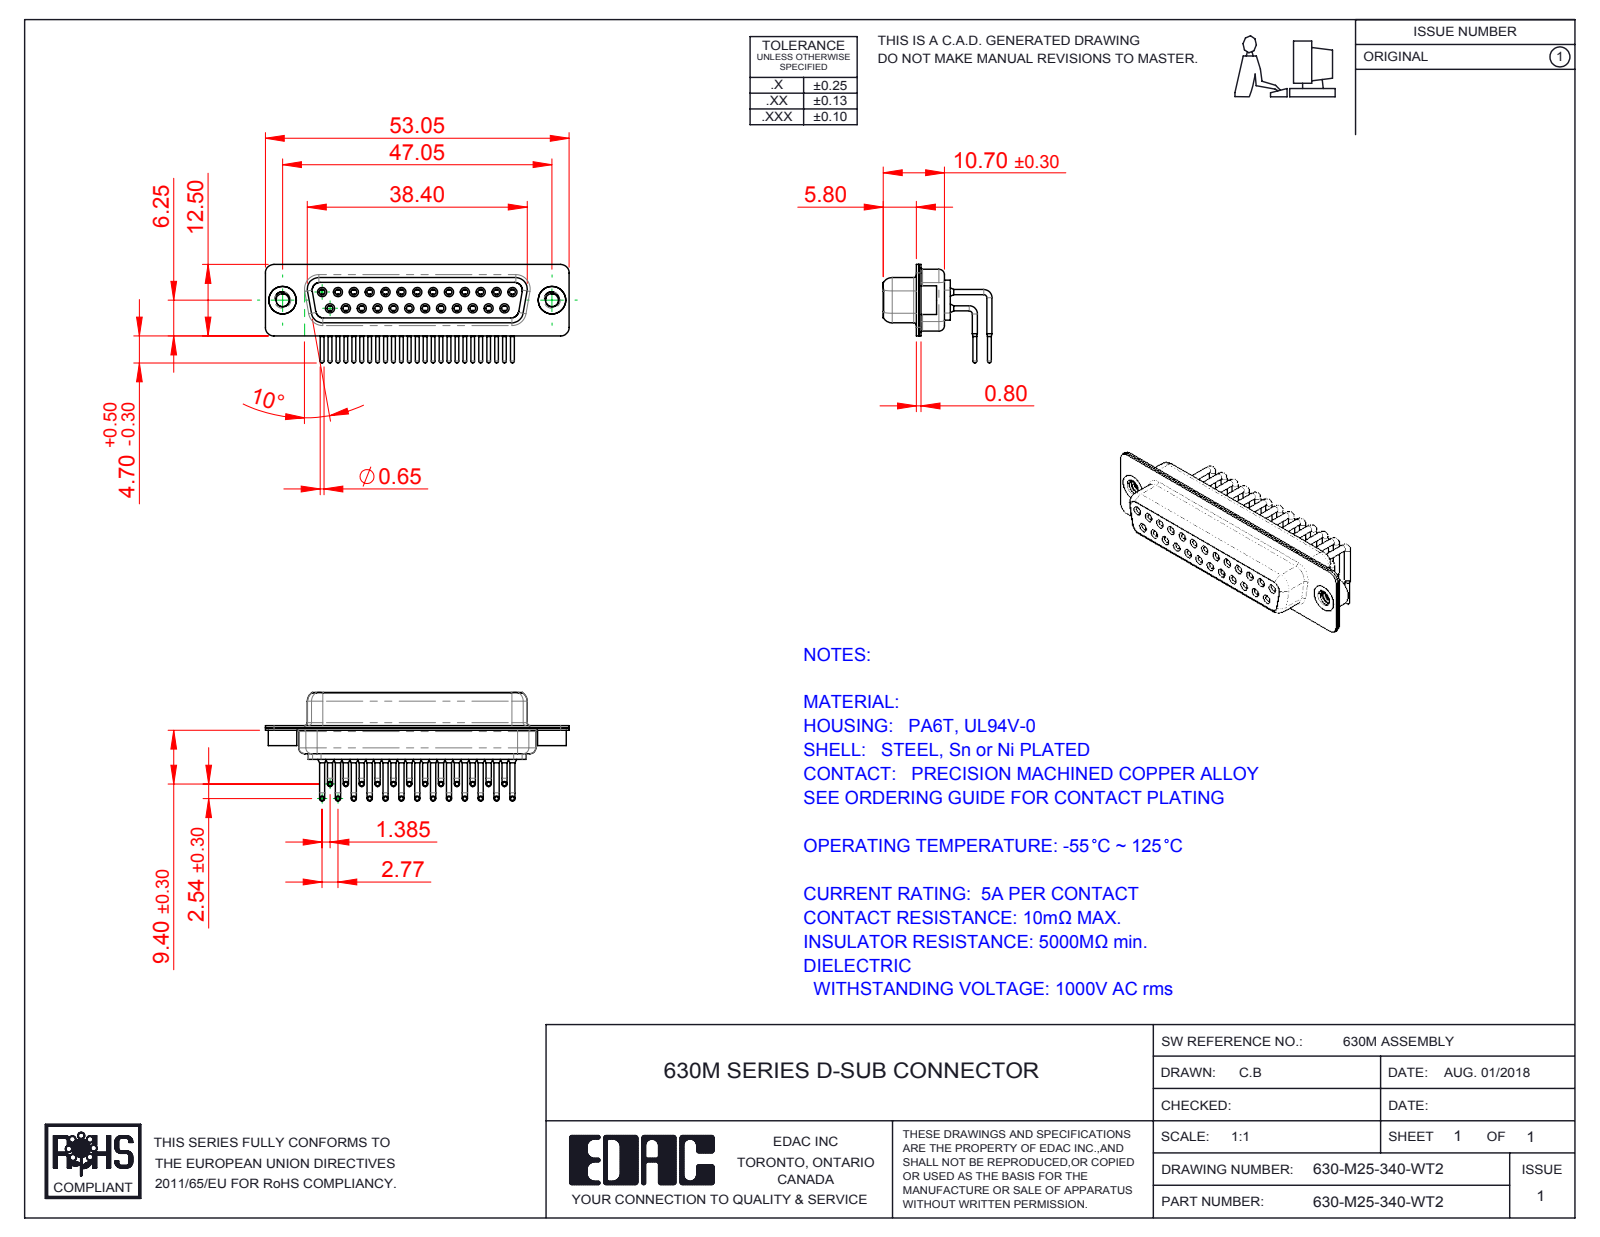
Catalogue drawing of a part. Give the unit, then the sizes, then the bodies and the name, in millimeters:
Units: millimetres
Overall size (bounding box): 53.05 × 18.99 × 17.2
Round holes (diameter × count): ⌀1 ×25, ⌀1.1 ×25, ⌀1.7 ×25, ⌀1.8 ×25, ⌀2 ×25, ⌀2.26 ×2, ⌀4 ×2, ⌀4.8 ×2
Round bosses / shafts (diameter × count): ⌀0.9 ×50, ⌀1.6 ×25, ⌀1.5 ×25, ⌀0.65 ×25, ⌀5 ×2, ⌀4.9 ×2
Partial cylindrical surfaces — rounded edges, fillets, slot ends (radius × count): R1.5 ×16, R2 ×12, R1.35 ×10, R1.6 ×8, R0.25 ×4, R0.5 ×4, R0.6 ×4, R0.65 ×4
Main face-to-face distances: 0.4, 1.45, 8.95, 6.2, 2.3, 1.9, 8.5, 7.05, 0.45, 0.85
Hole centre spacings: 3.16, 2.77, 5.54, 8.31, 11.08, 13.85, 5.04, 7.49
Volume: 3 898 mm³ · Surface area: 9 728 mm²
Bodies: 30 solids, 1604 faces (442 planar, 712 cylindrical, 450 other)
Part name (STEP PRODUCT): 630M Shell Rear_25 Contacts; 630-M25-340-WT2; 630M Contact Row 1; 630M Contact Row 2 (+3 more)
STEP written by: SolidWorks 2016 (CONFIG_CONTROL_DESIGN)
